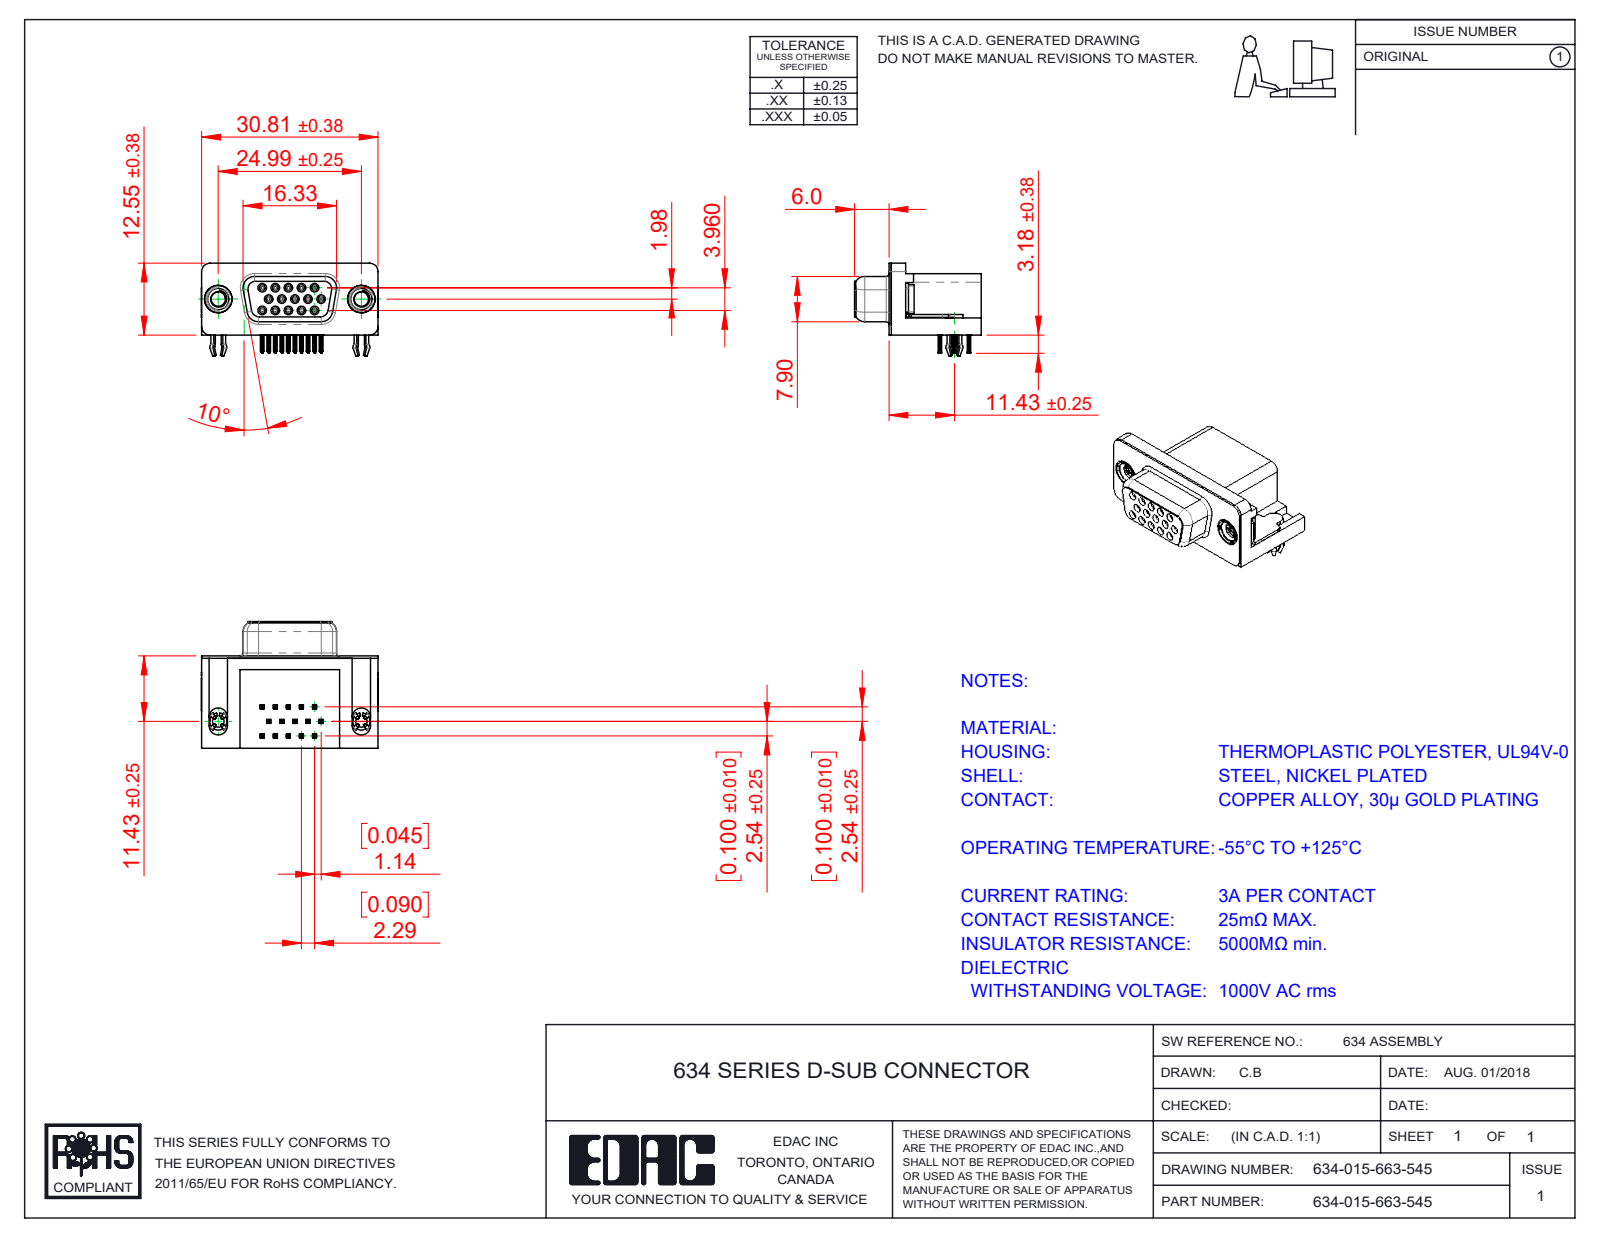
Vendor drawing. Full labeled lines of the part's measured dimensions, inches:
Part name (STEP PRODUCT): Contact Top; Contact Bottom; Contact Middle; 4 Prong Board Lock (+4 more)
STEP written by: SolidWorks 2016 (CONFIG_CONTROL_DESIGN)
Units: inches
Bodies: 21 solids, 2541 faces (1108 planar, 609 cylindrical, 824 other)
Overall size (bounding box): 1.216 × 0.87 × 0.64
Volume: 0.278 in³ · Surface area: 10.2 in²
Round holes (diameter × count): ⌀0.031 ×15, ⌀0.035 ×15, ⌀0.079 ×2, ⌀0.098 ×2, ⌀0.157 ×2, ⌀0.189 ×2, ⌀0.197 ×2
Round bosses / shafts (diameter × count): ⌀0.047 ×15, ⌀0.193 ×2, ⌀0.187 ×2, ⌀0.154 ×2, ⌀0.118 ×2
Partial cylindrical surfaces — rounded edges, fillets, slot ends (radius × count): R0.004 ×120, R0.006 ×60, R0.014 ×30, R0.039 ×19, R0.013 ×15, R0.01 ×12, R0.053 ×8, R0.063 ×8
Main face-to-face distances: 0.016, 0.407, 0.618, 0.634, 0.014, 0.098, 0.114, 0.024, 0.252, 0.421
Hole centre spacings: 0.09, 0.09, 0.156, 0.18, 0.238, 0.156, 0.18, 0.27
